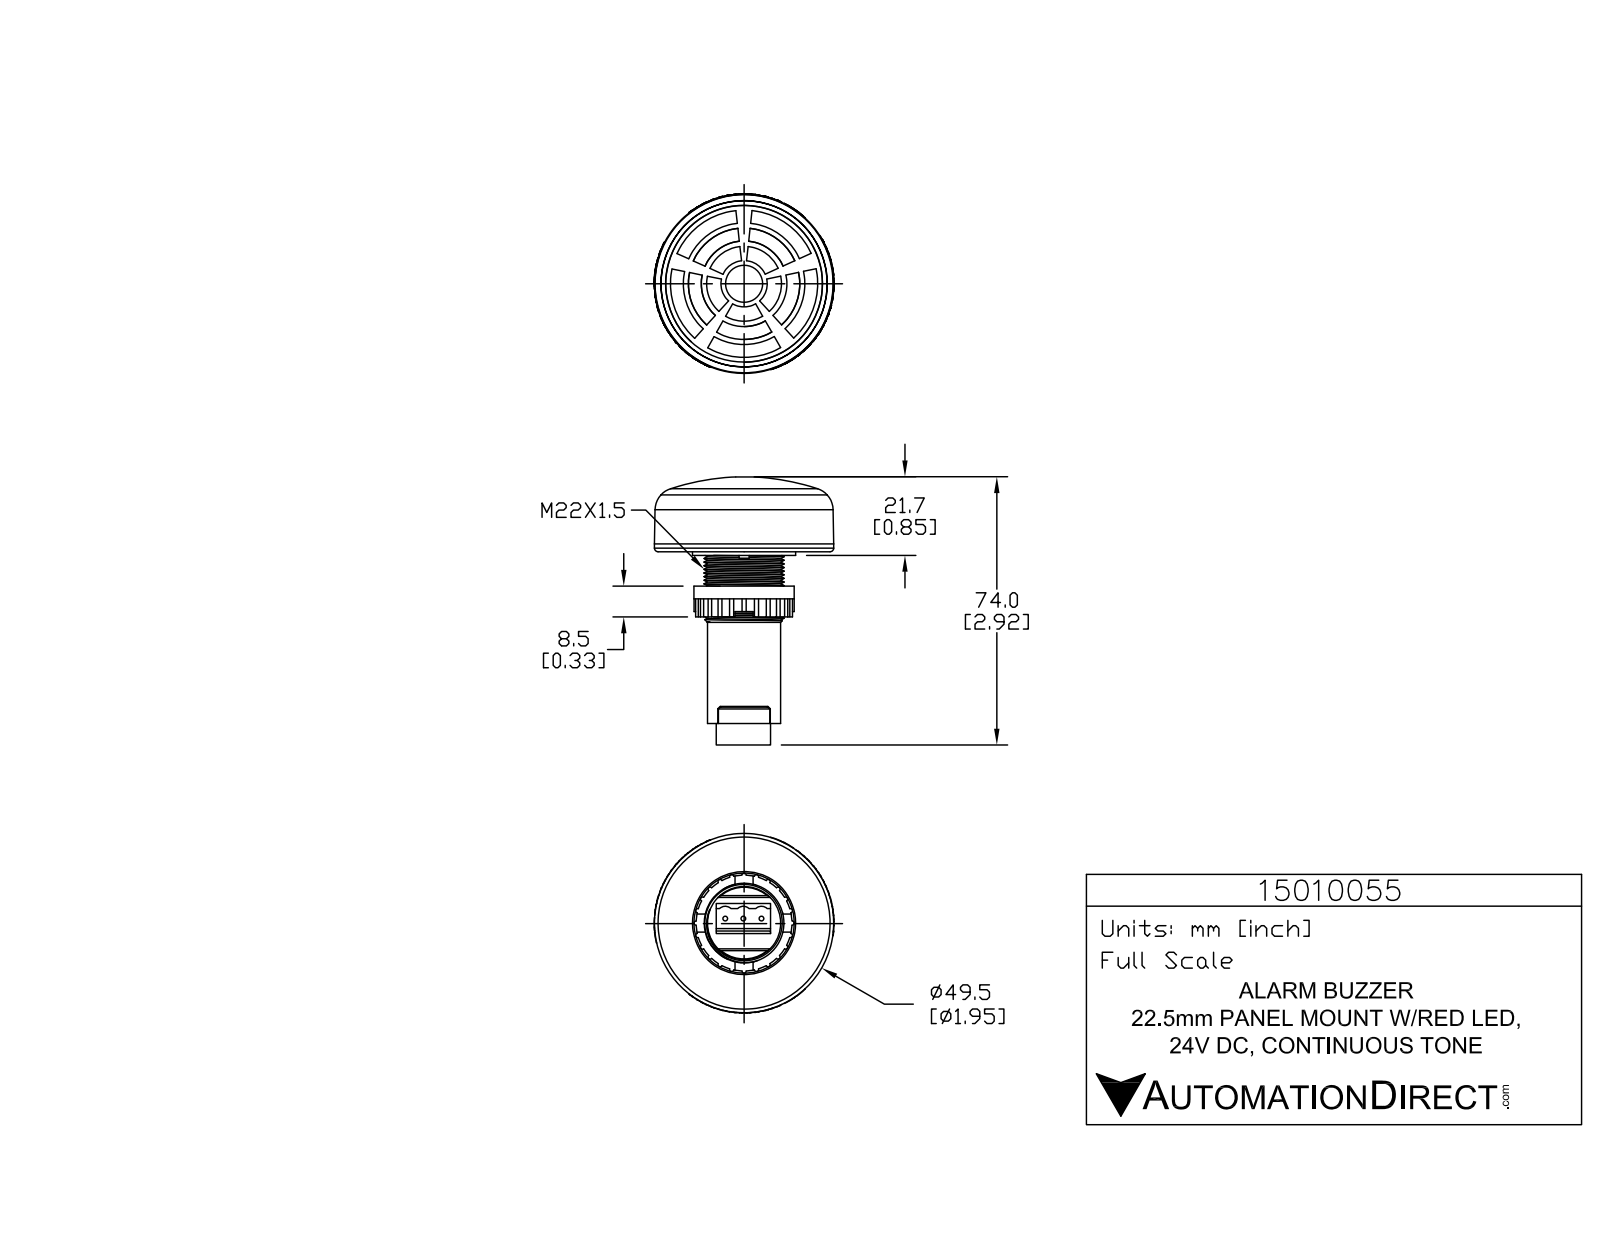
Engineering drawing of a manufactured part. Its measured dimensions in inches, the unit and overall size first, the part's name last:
Units: inches
Overall size (bounding box): 2.823 × 1.956 × 1.952
Round holes (diameter × count): ⌀0.039 ×4
Round bosses / shafts (diameter × count): ⌀0.226 ×4, ⌀0.056 ×4, ⌀0.051 ×3, ⌀1.949 ×1, ⌀1.807 ×1, ⌀1.122 ×1, ⌀1.091 ×1, ⌀0.866 ×1
Partial cylindrical surfaces — rounded edges, fillets, slot ends (radius × count): R0.023 ×24, R0.008 ×8, R0.008 ×8, R0.008 ×8, R0.131 ×8, R0.004 ×4, R0.005 ×4, R0.008 ×4
Main face-to-face distances: 0.335, 0.374, 0.039, 1.398, 1.732, 1.772, 0.709, 1.063, 0.669, 1.297
Volume: 3.113 in³ · Surface area: 19.88 in²
Bodies: 1 solid, 1200 faces (744 planar, 322 cylindrical, 134 other)
Part name (STEP PRODUCT): 15010055
STEP written by: SolidWorks 2017 (AUTOMOTIVE_DESIGN)
